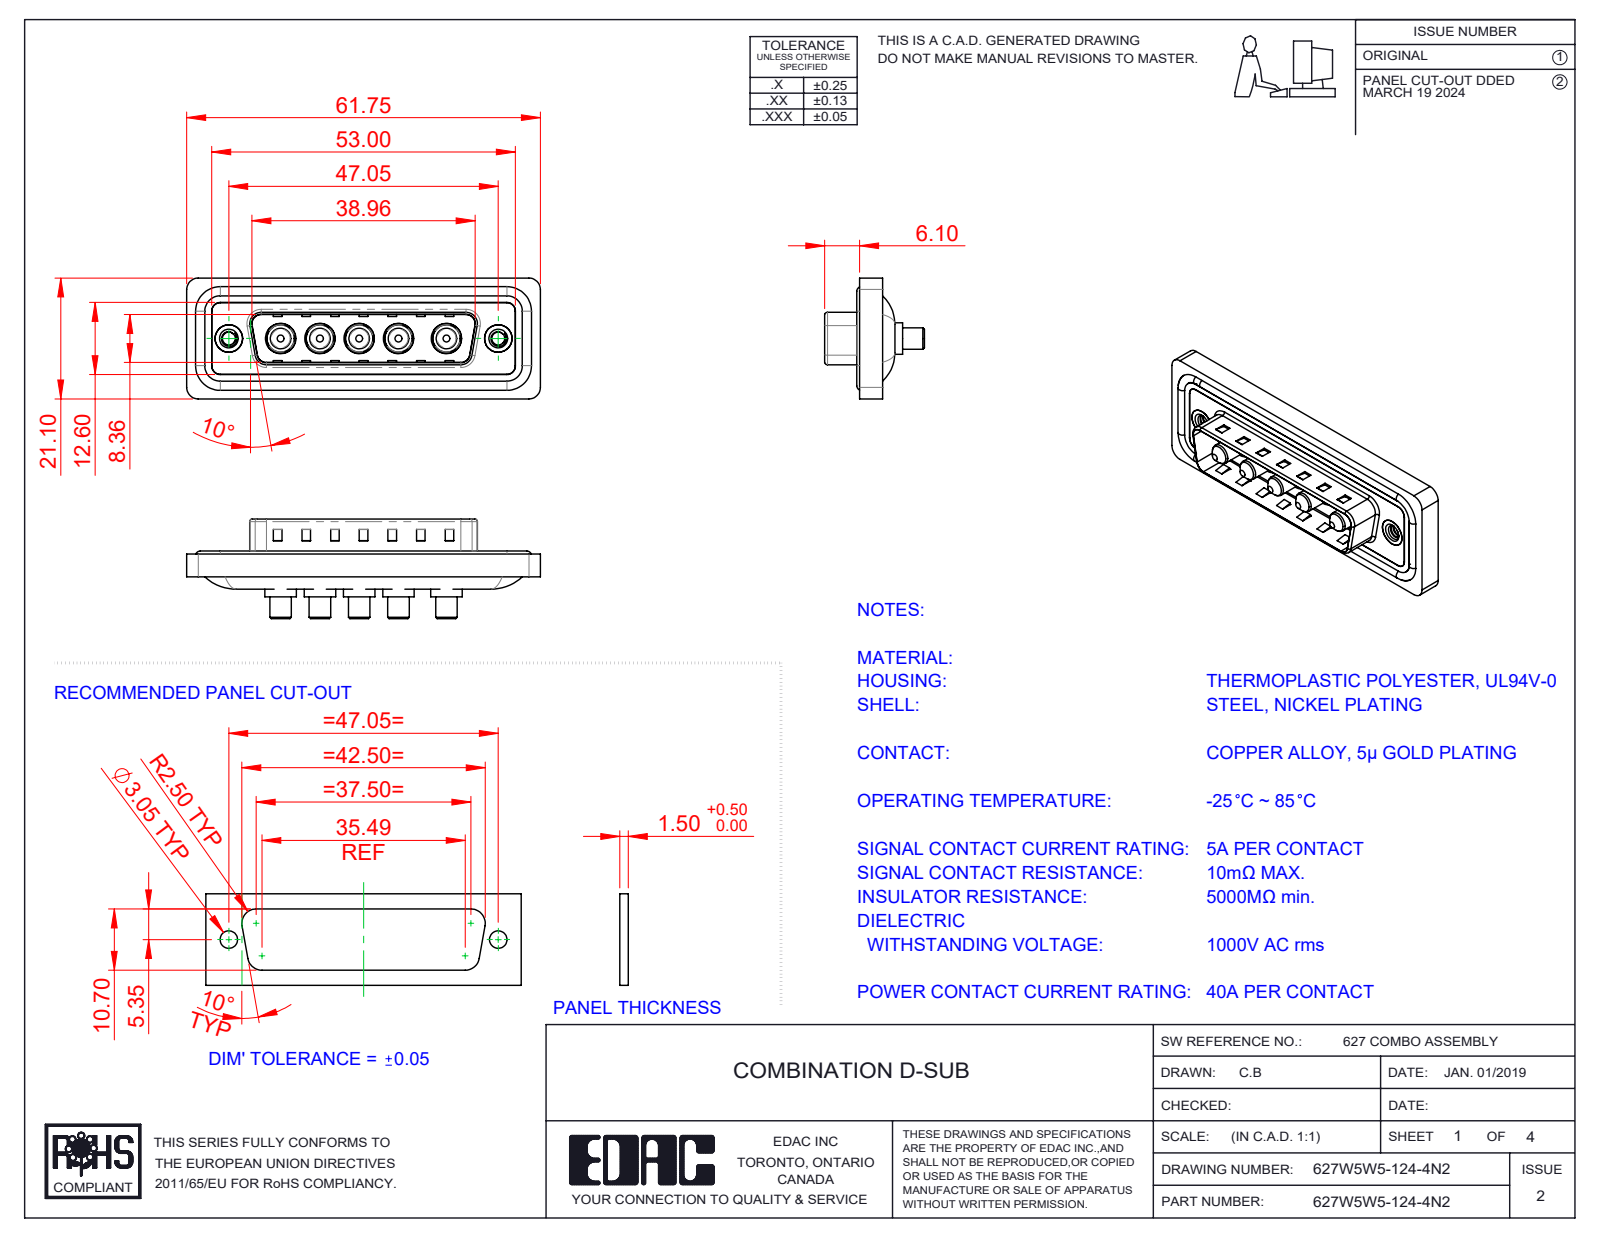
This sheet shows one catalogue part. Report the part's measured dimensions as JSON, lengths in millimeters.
{"part_name": "627Combo Housing_5W5; 627Combo Waterproof Housing_25 Contacts; Power Pin_40A S; 627Combo Shell Rear_25 Contacts (+3 more)", "step_written_by": "SolidWorks 2023 (CONFIG_CONTROL_DESIGN)", "units": "millimeters", "bodies": {"solids": 17, "faces": 678, "planar": 259, "cylindrical": 283, "other": 136}, "overall_size": [61.75, 21.1, 17.4], "volume_mm3": 7565, "surface_area_mm2": 11851, "round_holes": [[4.85, 5], [5.3, 5], [2.26, 2], [4, 2], [4.8, 2], [5, 2]], "round_bosses_or_shafts": [[5.5, 5], [5.2, 5], [4.75, 5], [3.75, 5], [3.6, 5], [1.6, 4], [4.9, 2]], "partial_cylinders_radius": [[1.5, 22], [2, 18], [0.5, 8], [1.6, 8], [2.1, 5], [0.25, 4], [0.6, 4], [0.65, 4]], "face_to_face_distances": [0.4, 1.5, 0.5, 1.1, 3.1, 1.6, 2.9, 0.82, 9.58, 5.65], "hole_center_spacings": [6.86, 9.04, 13.73, 38.01, 6.87, 8.37, 8.38, 9.05]}
